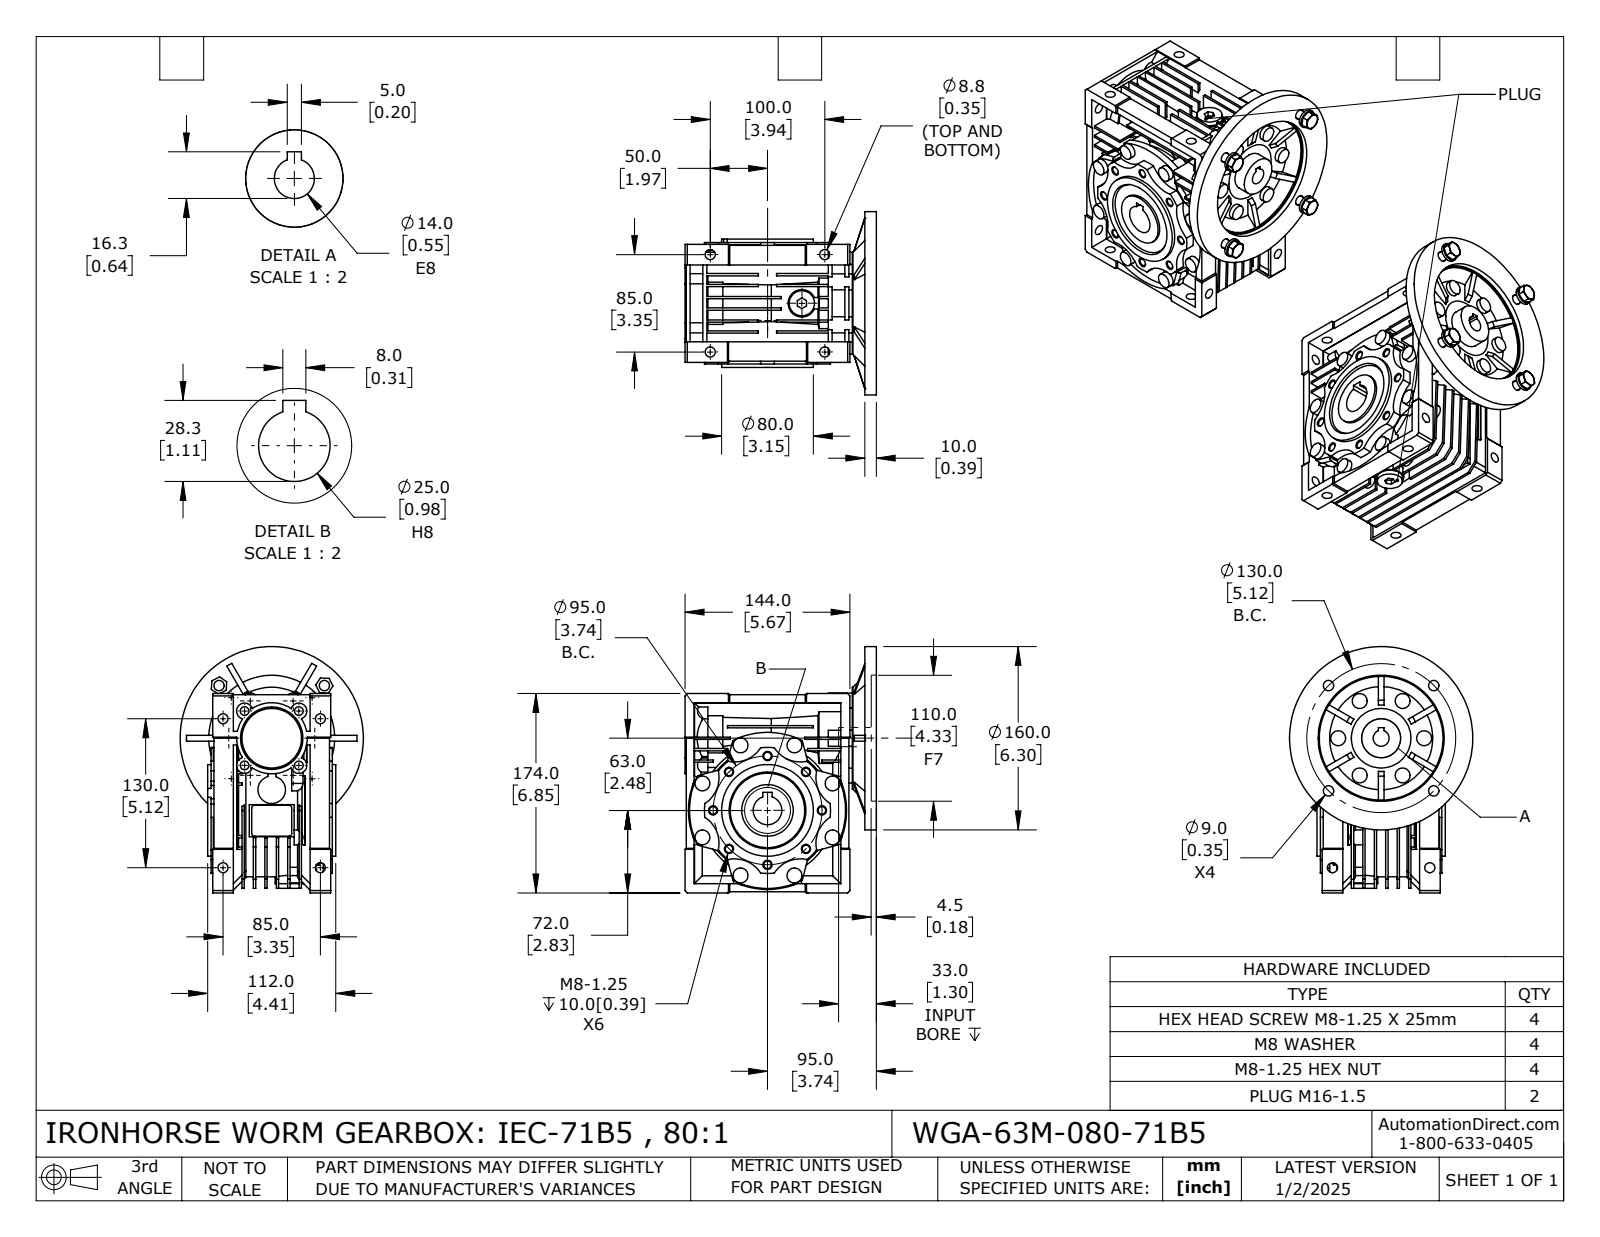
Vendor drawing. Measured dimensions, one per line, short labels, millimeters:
name: WGA-63M-080-71B5
written by: SolidWorks 2024 (CONFIG_CONTROL_DESIGN)
unit: mm
bodies: 20 solids, 1516 faces (887 planar, 379 cylindrical, 250 other)
size: 215 × 182.98 × 160
volume: 1 919 000 mm³; area: 371 344 mm²
holes: 8× ⌀6.65, 8× ⌀8.78, 4× ⌀6.8, 4× ⌀7.56, 4× ⌀8, 4× ⌀9, 4× ⌀9.12, 2× ⌀14.5, 1× ⌀14, 1× ⌀15, 1× ⌀25, 1× ⌀34
bosses: 14× ⌀13, 4× ⌀16, 3× ⌀24, 2× ⌀22, 2× ⌀15.8, 2× ⌀13.7, 1× ⌀160, 1× ⌀110
rounds: 10× R7, 8× R27, 4× R2.5, 1× R8.35, 1× R29.5, 1× R30.5, 1× R42, 1× R58
face distances: 10, 8, 20, 2, 30, 12, 7, 18, 40, 1
hole spacings: 36.36, 47.5, 67.18, 73.12, 87.77, 31.49, 33.5, 47.38
